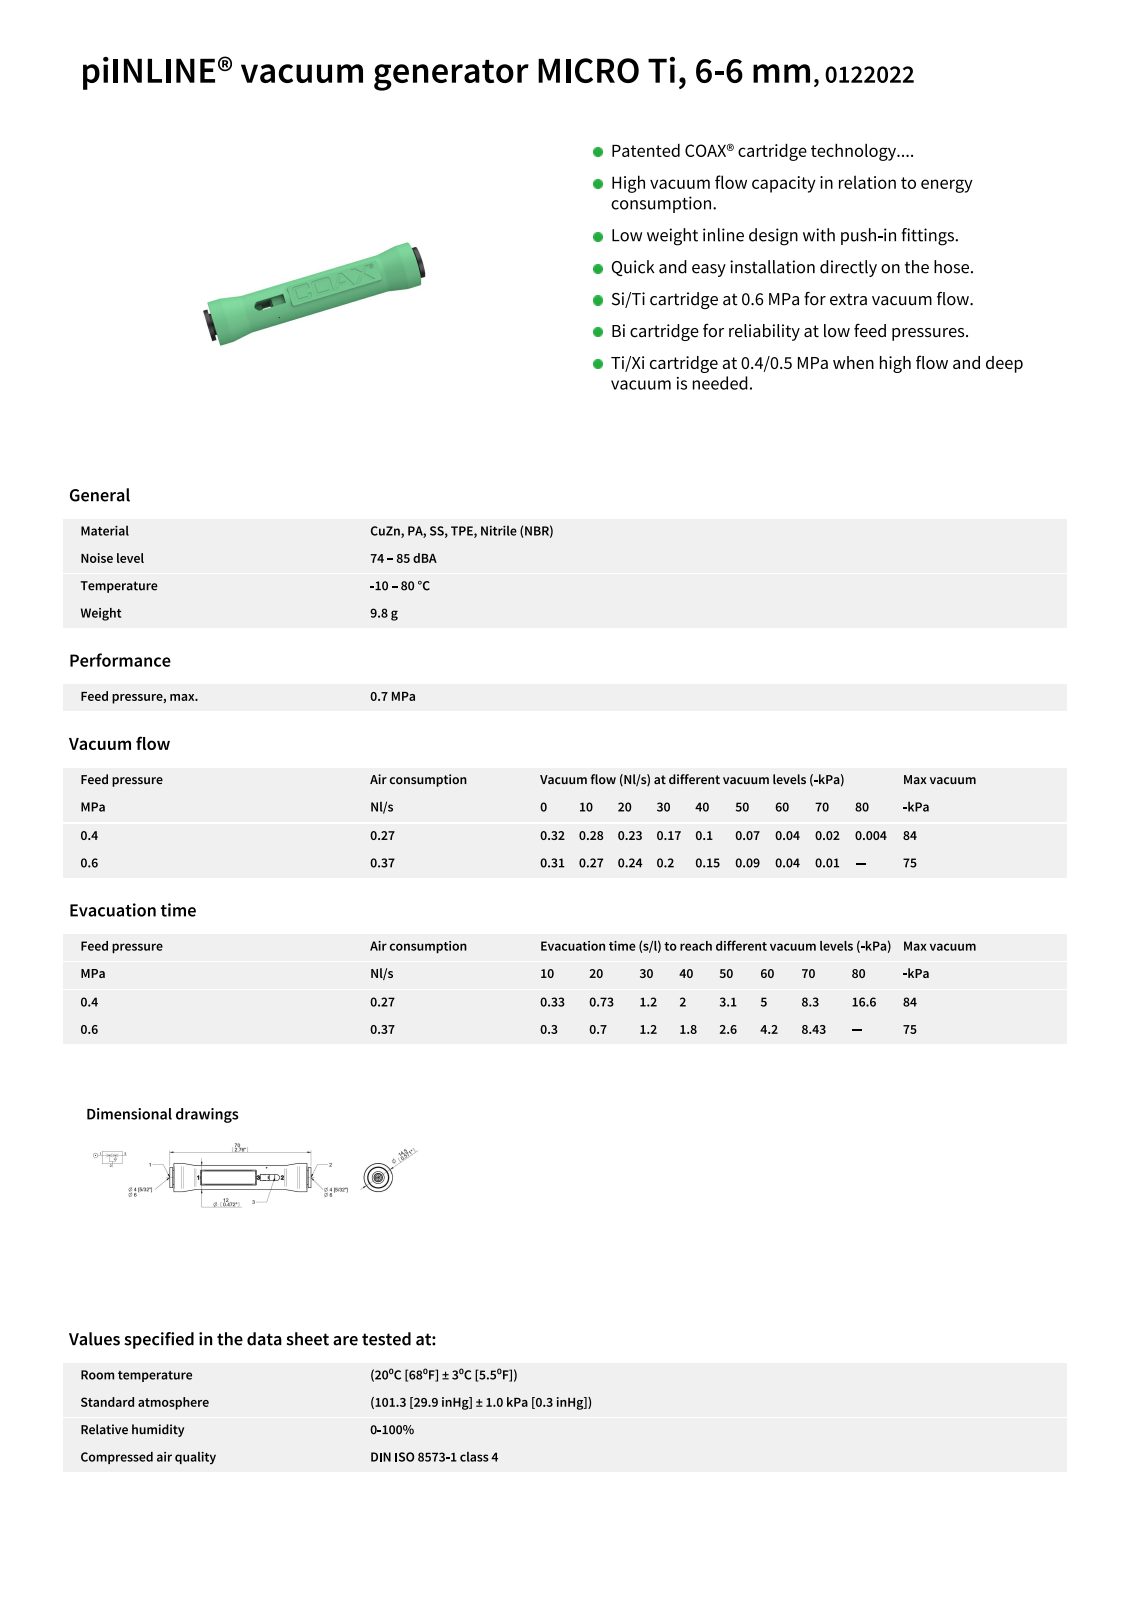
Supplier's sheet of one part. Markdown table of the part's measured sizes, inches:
| quantity | value |
| --- | --- |
| part name | 0122022 |
| STEP written by | ST-DEVELOPER v16.7 (AUTOMOTIVE_DESIGN) |
| units | inches |
| bodies | 1 solid, 135 faces (63 planar, 24 cylindrical, 48 other) |
| overall size | 2.756 × 0.559 × 0.559 |
| volume | 0.504 in³ |
| surface area | 5.165 in² |
| round holes (diameter × count) | 0.236 × 1 |
| round bosses / shafts (diameter × count) | 0.559 × 1, 0.472 × 1, 0.394 × 1, 0.276 × 1 |
| partial cylindrical surfaces (radius × count) | 0.217 × 1, 0.246 × 1 |
| main face-to-face distances | 2.598, 0.079, 2.677, 0.055, 2.701, 0.024, 2.622, 2.756, 2.646, 0.118 |
